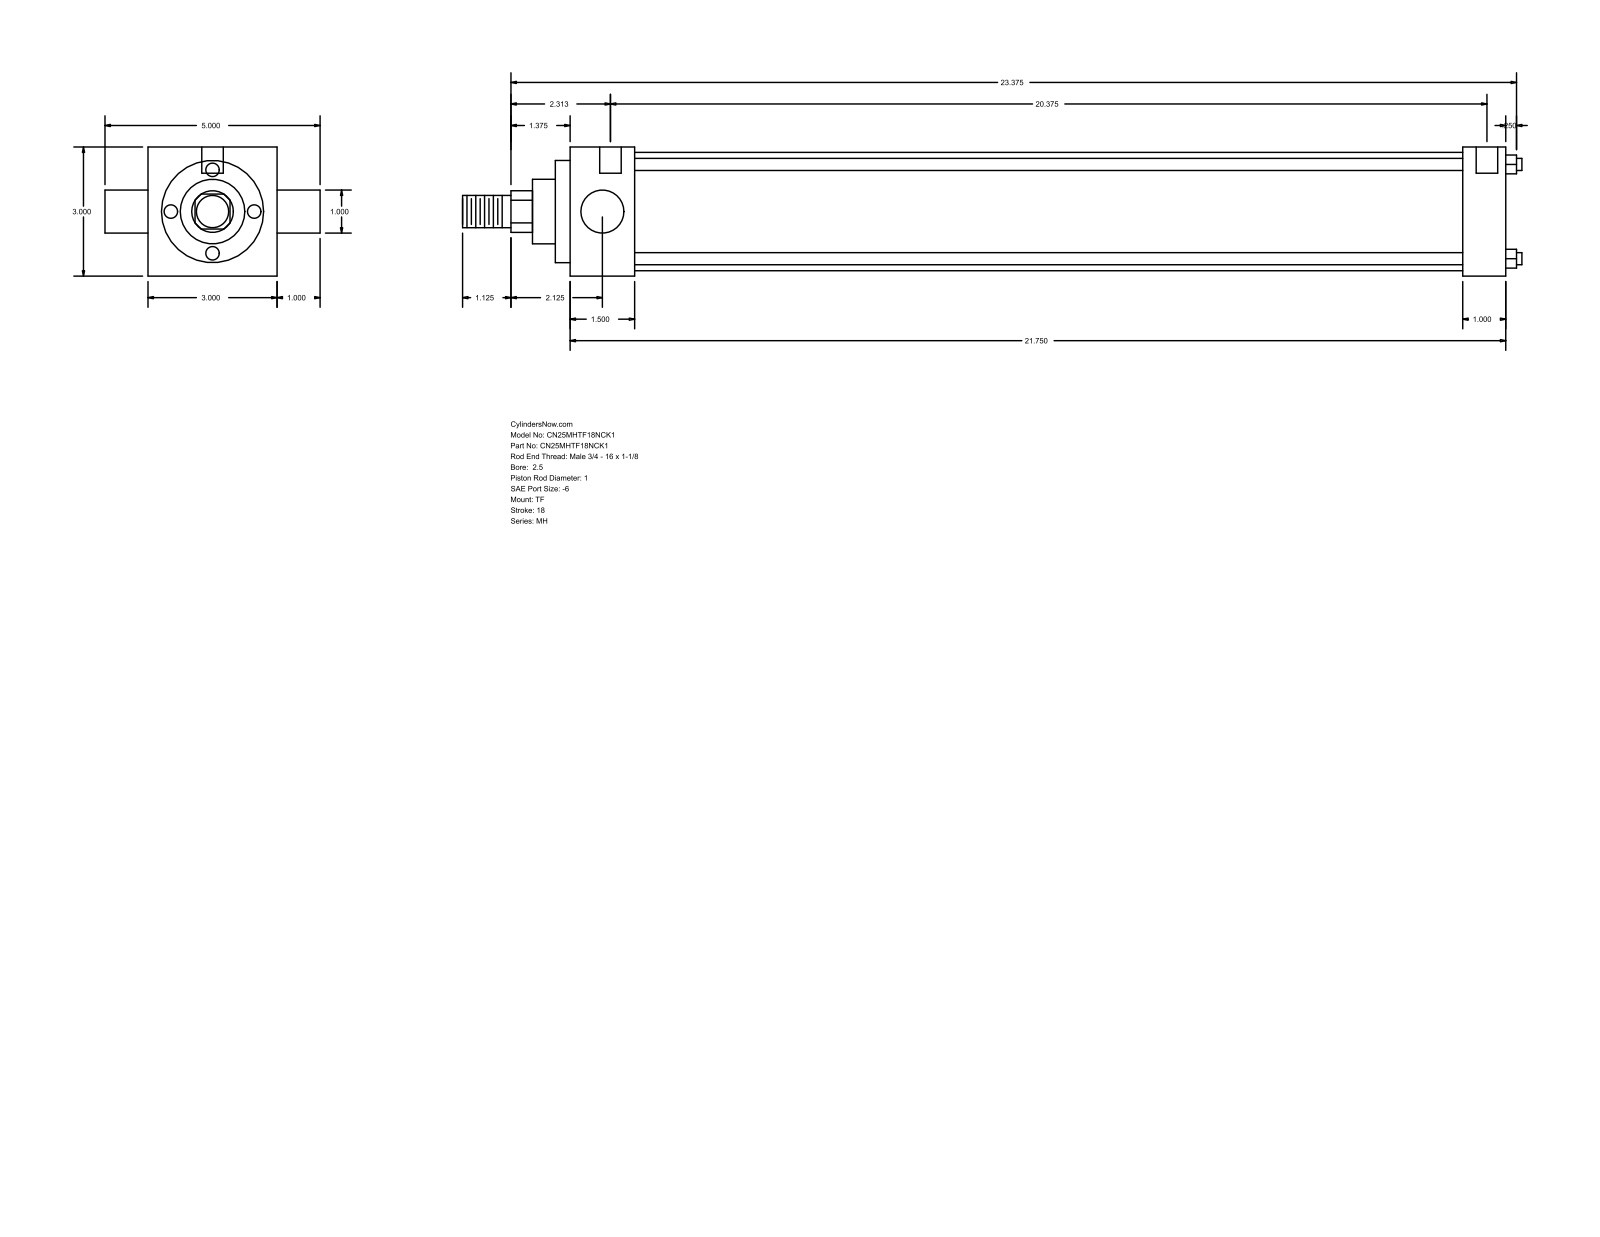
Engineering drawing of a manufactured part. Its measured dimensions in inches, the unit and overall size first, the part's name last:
Units: inches
Overall size (bounding box): 24.625 × 5 × 3
Round holes (diameter × count): ⌀0.219 ×3, ⌀0.5 ×2
Round bosses / shafts (diameter × count): ⌀0.281 ×4, ⌀1 ×2, ⌀2.75 ×1, ⌀2.375 ×1, ⌀1.5 ×1, ⌀0.75 ×1
Partial cylindrical surfaces — rounded edges, fillets, slot ends (radius × count): R0.484 ×1
Main face-to-face distances: 3, 21.75, 1, 1.5, 20.25, 20.75, 19.25, 0.344, 1.844, 21.094
Hole centre spacings: 0.125, 0.187, 20.375, 20.5, 20.562, 20.687
Bodies: 0 solids, 86 faces (61 planar, 25 cylindrical, 0 other)
Part name (STEP PRODUCT): MH_TF__0250_1
STEP written by: GSSL Pune (CONFIG_CONTROL_DESIGN)
